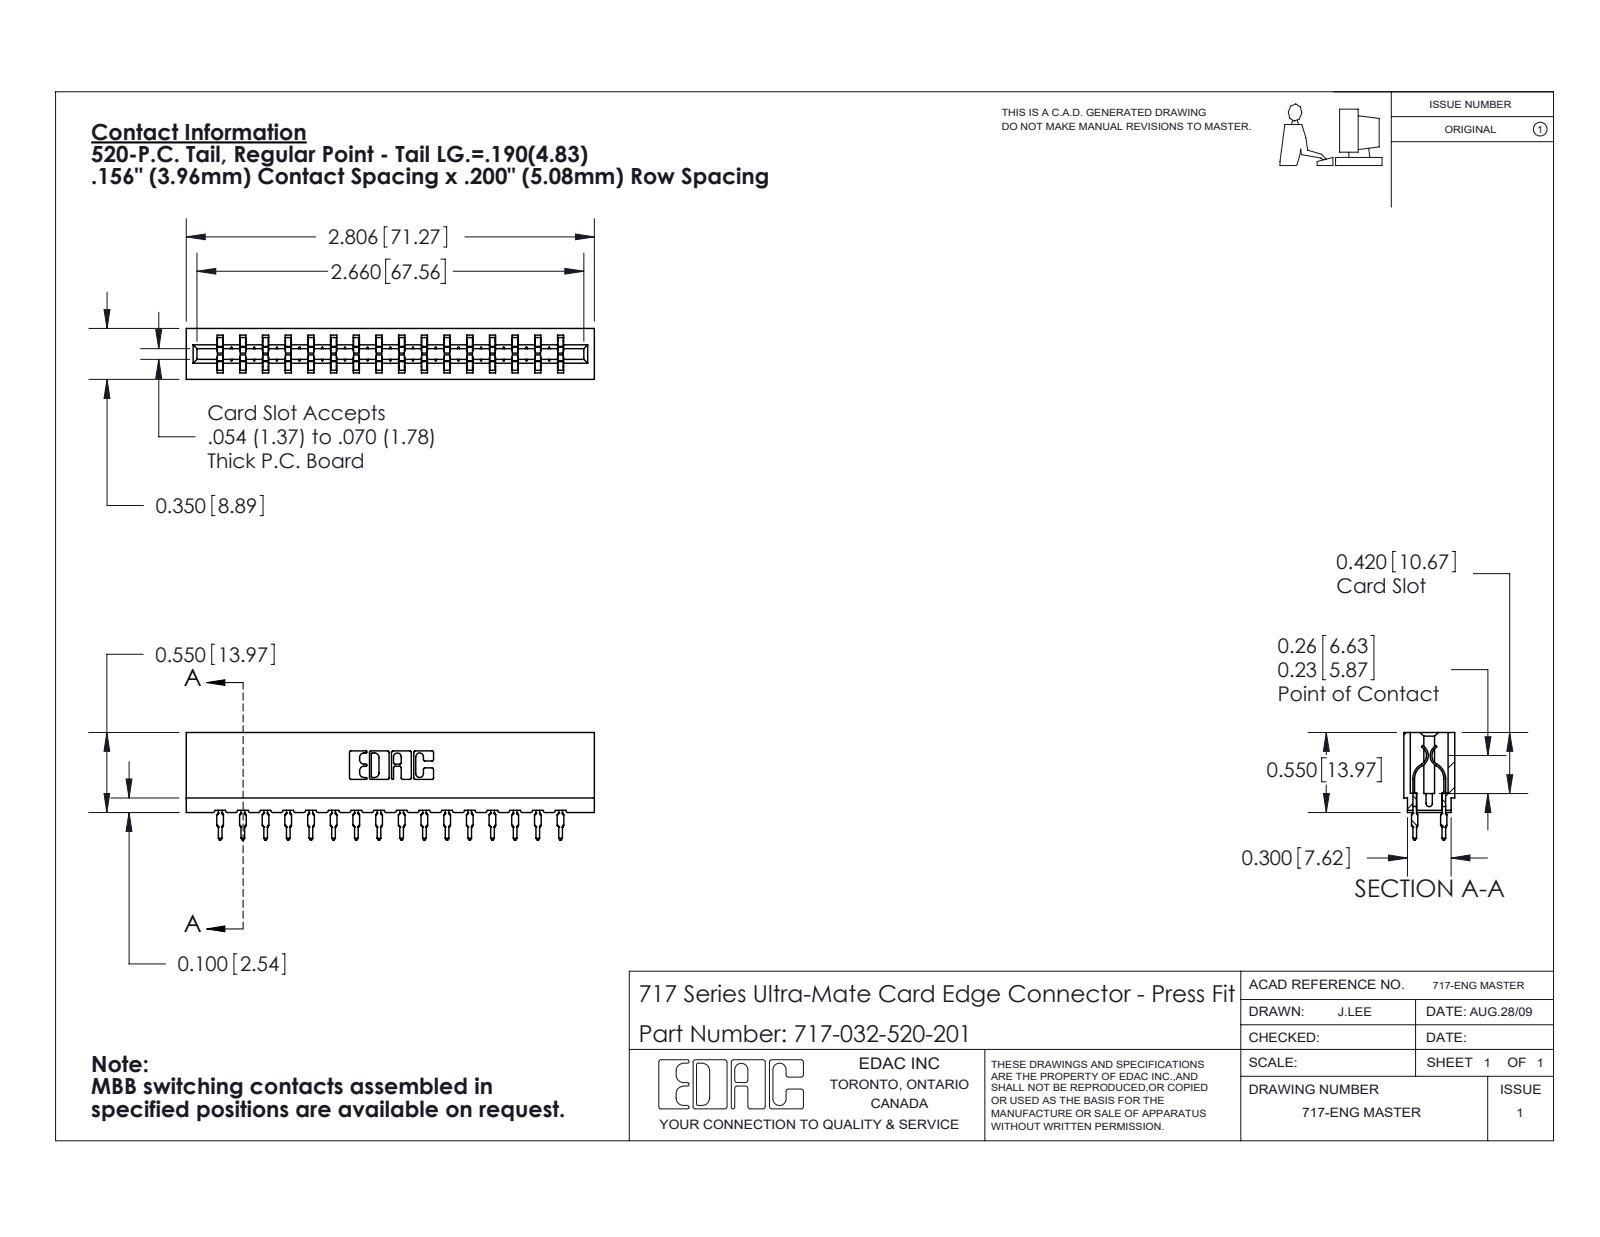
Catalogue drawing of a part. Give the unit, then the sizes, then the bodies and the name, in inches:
Units: inches
Overall size (bounding box): 2.806 × 0.739 × 0.35
Partial cylindrical surfaces — rounded edges, fillets, slot ends (radius × count): R0.021 ×64, R0.015 ×32, R0.01 ×22, R0.005 ×8, R0.011 ×8, R0.007 ×6, R0.031 ×6, R0.026 ×3
Main face-to-face distances: 0.212, 0.138, 0.35, 0.156, 0.468, 0.624, 0.198, 0.312, 0.074, 0.063
Volume: 0.382 in³ · Surface area: 14.04 in²
Bodies: 33 solids, 2974 faces (1542 planar, 600 cylindrical, 832 other)
Part name (STEP PRODUCT): 745-292-001_520; 717 Part_Insulator Option - 06; 717-032-520-201
STEP written by: SolidWorks 2020 (CONFIG_CONTROL_DESIGN)
